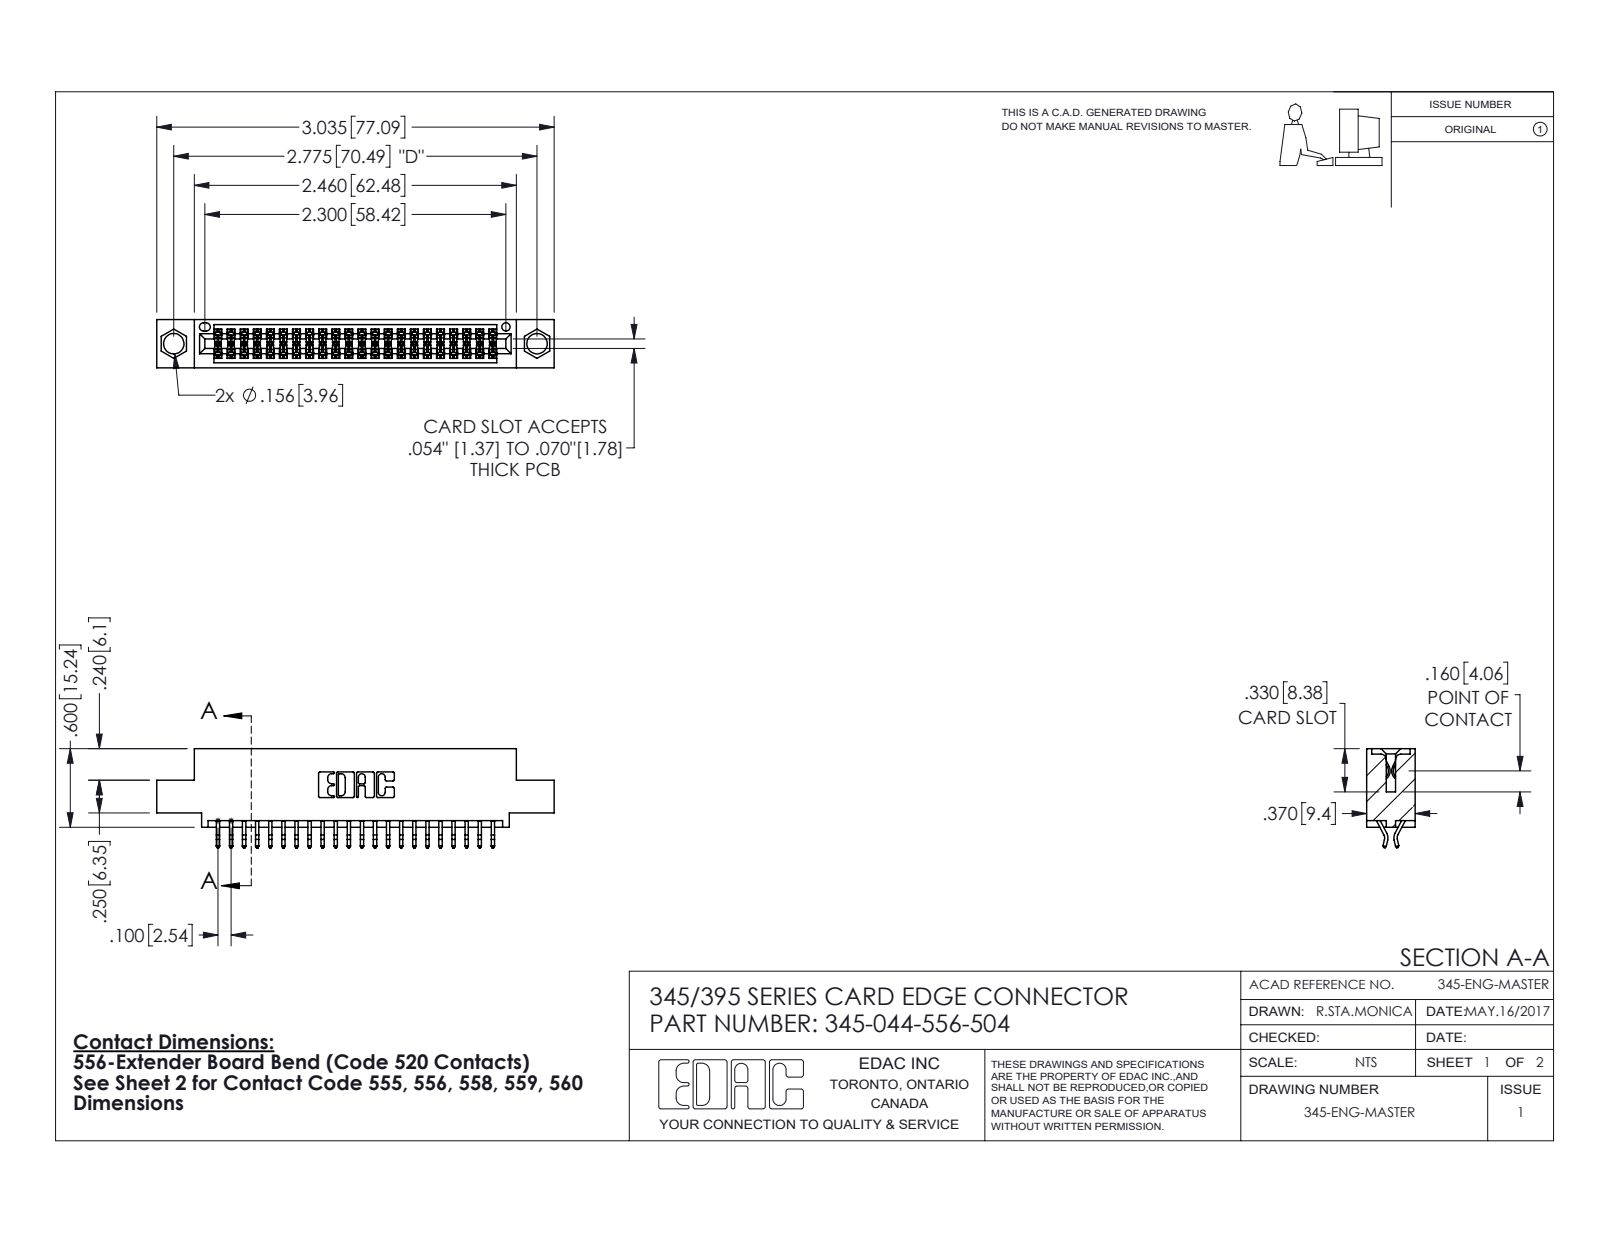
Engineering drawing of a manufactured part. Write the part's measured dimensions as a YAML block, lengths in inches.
part_name: "345 Part_0.110 Offset - 0.156 Dia-TI; 345-044-556-504; 345-292-001_556 Tail"
step_written_by: "SolidWorks 2020 (CONFIG_CONTROL_DESIGN)"
units: inches
bodies: {solids: 45, faces: 2608, planar: 1726, cylindrical: 882, other: 0}
overall_size: [3.035, 0.757, 0.37]
volume: 0.435
surface_area: 15.57
round_holes:
  - {diameter: 0.156, count: 2}
  - {diameter: 0.064, count: 1}
partial_cylinders:
  - {radius: 0.006, count: 88}
  - {radius: 0.01, count: 22}
  - {radius: 0.007, count: 6}
  - {radius: 0.031, count: 6}
  - {radius: 0.026, count: 3}
  - {radius: 0.01, count: 2}
  - {radius: 0.014, count: 2}
  - {radius: 0.019, count: 2}
face_to_face_distances: [0.298, 0.072, 0.37, 0.2, 0.025, 0.098, 0.272, 0.225, 0.175, 0.149]
hole_center_spacings: [0.27, 2.541, 2.775]
